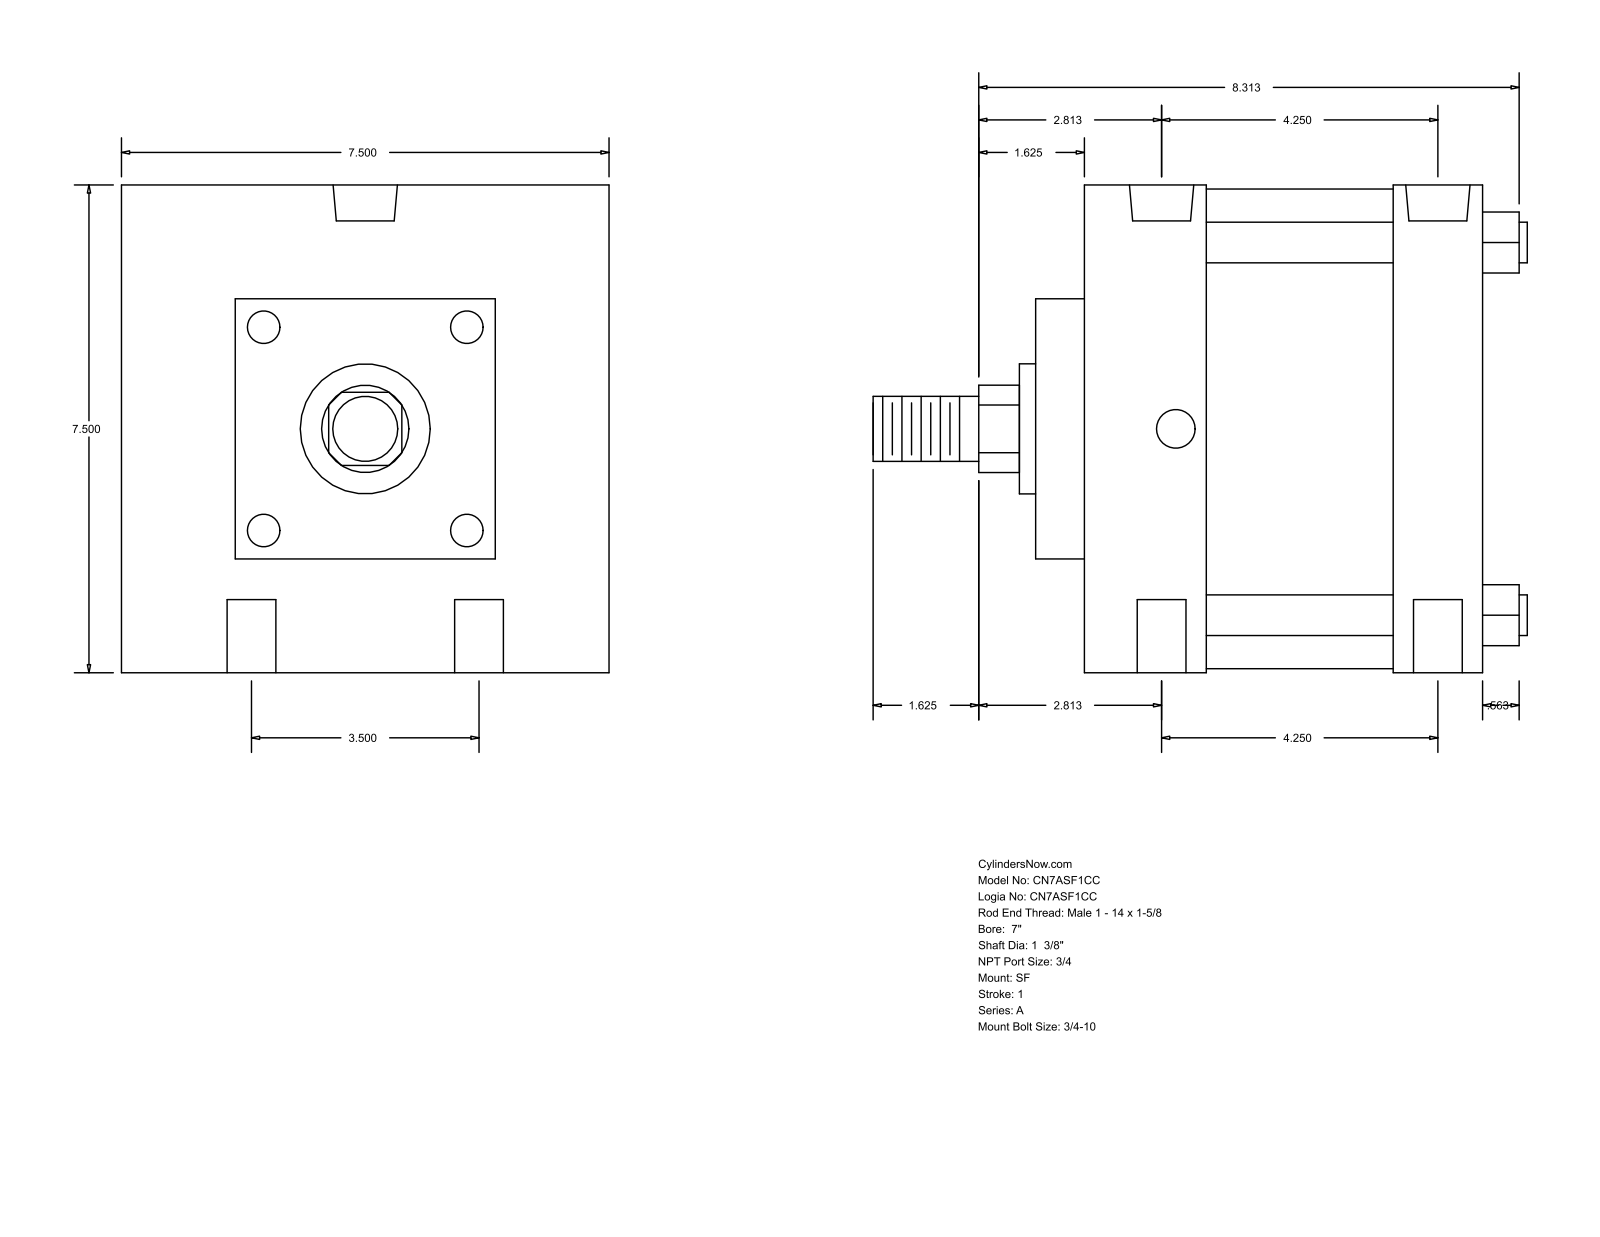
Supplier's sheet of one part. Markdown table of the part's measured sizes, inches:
| quantity | value |
| --- | --- |
| part name | A_SF__0700_1.375 |
| STEP written by | GSSL Pune (CONFIG_CONTROL_DESIGN) |
| units | inches |
| bodies | 0 solids, 93 faces (67 planar, 26 cylindrical, 0 other) |
| overall size | 10.063 × 7.5 × 7.5 |
| round holes (diameter × count) | 0.75 × 4, 0.594 × 2, 0.989 × 2 |
| round bosses / shafts (diameter × count) | 0.625 × 4, 7.375 × 1, 2 × 1, 1.375 × 1, 1 × 1 |
| partial cylindrical surfaces (radius × count) | 0.672 × 1 |
| main face-to-face distances | 7.5, 6.125, 5.75, 0.75, 6.875, 2.625, 5.5, 1.875, 4.75, 2.875 |
| hole center spacings | 1.75, 4.596, 4.25, 3.5, 5.506, 3.812 |
